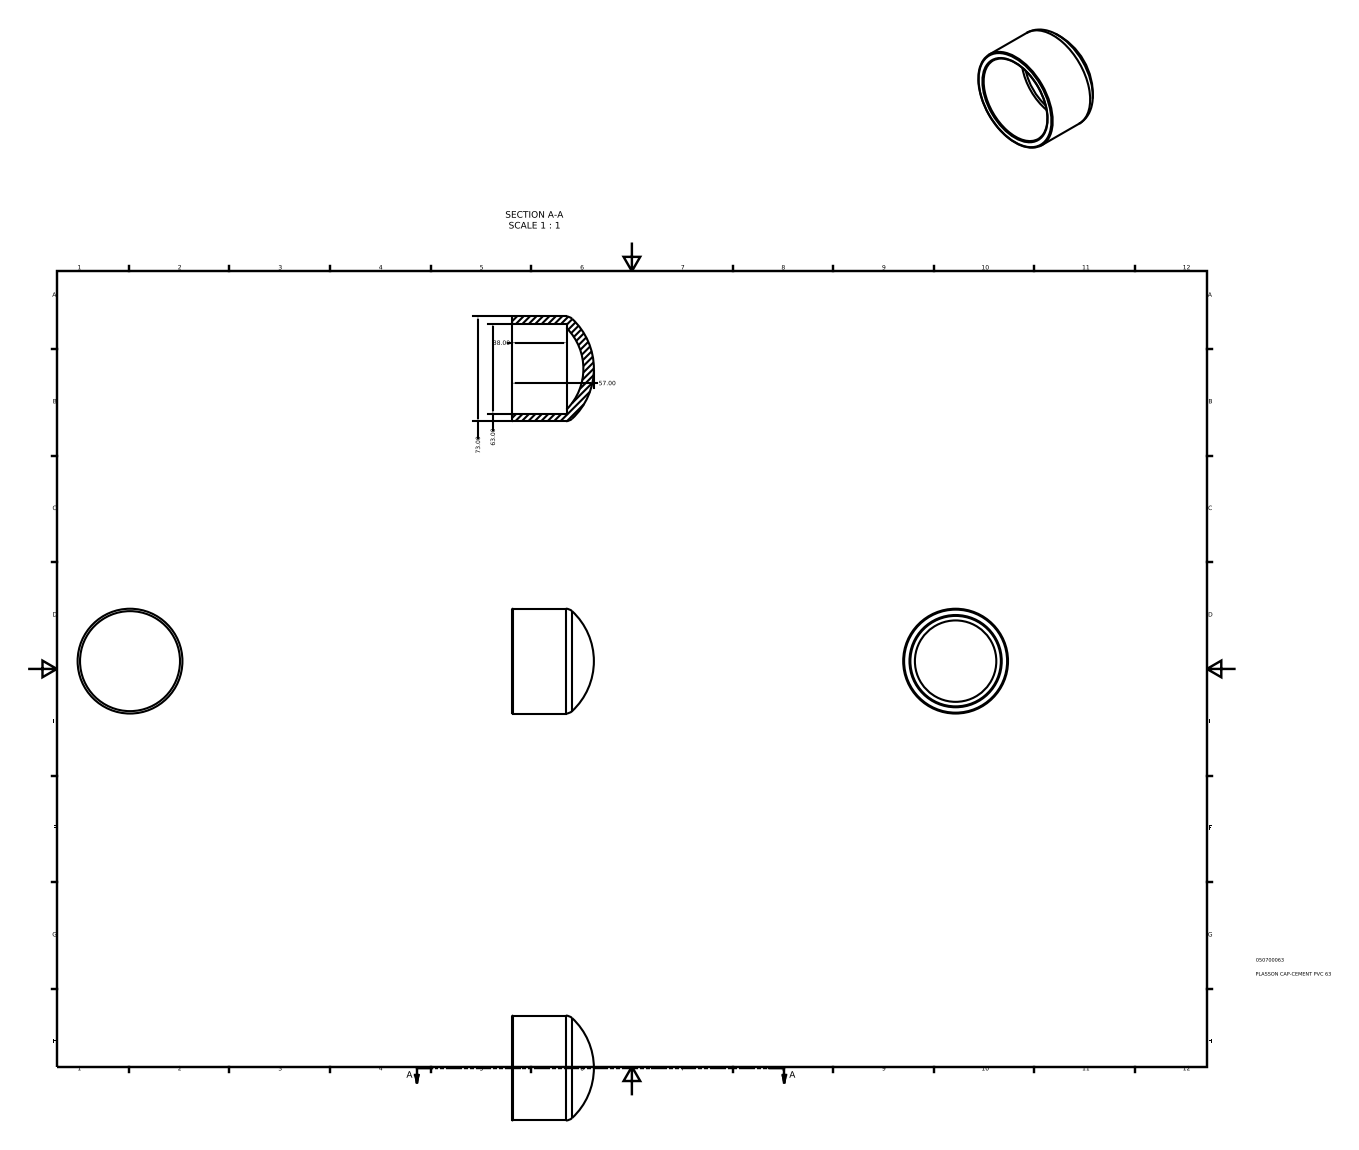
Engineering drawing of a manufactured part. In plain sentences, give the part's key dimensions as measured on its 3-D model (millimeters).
The part is named "050700063". Its 3-D file was written by "Autodesk Inventor 2015 (AUTOMOTIVE_DESIGN)". It is 1 solid with 9 faces: 2 planar, 2 cylindrical and 5 other. Overall it measures 73 by 73 by 57 millimeters. Its volume is 71 146 cubic millimeters and its surface area 26 224 square millimeters. Round holes: 1 of diameter 63. Round bosses or shafts: 1 of diameter 73. The main face-to-face distances are 38.
